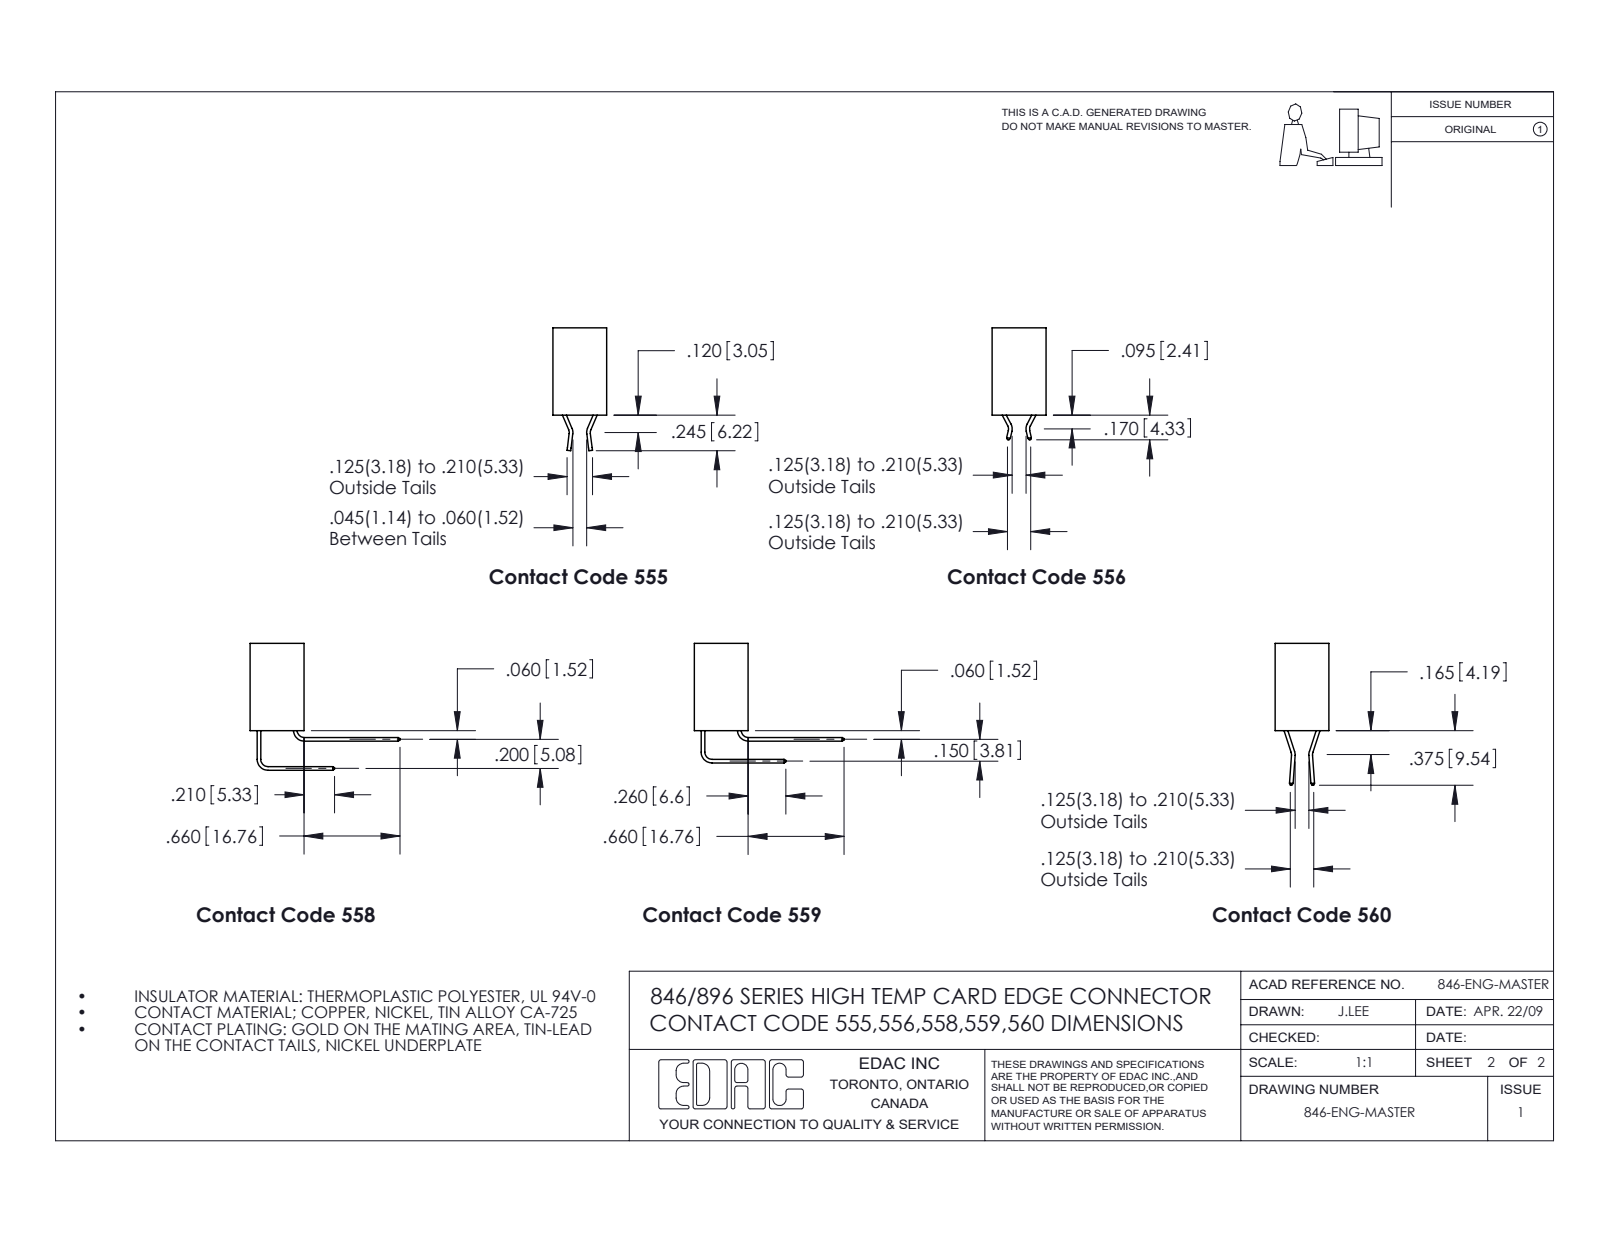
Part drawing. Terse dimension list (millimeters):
name: 345-250-001_345-250-005-103; 346 Part_Flush Mounting Lugs - 0.156 Dia-TI; 346-031-558-107; 345-292-001_558 Tail - 2
written by: SolidWorks 2016 (CONFIG_CONTROL_DESIGN)
unit: mm
bodies: 34 solids, 2042 faces (1410 planar, 616 cylindrical, 16 other)
size: 119 × 22.2 × 14.7
volume: 11 400 mm³; area: 14 790 mm²
holes: 2× ⌀2.5, 2× ⌀3.2, 2× ⌀4, 1× ⌀1.6
bosses: 2× ⌀3.9
rounds: 62× R0.2, 22× R0.3, 6× R0.2, 6× R0.8, 3× R0.7, 2× R0.8, 2× R1, 1× R0.4
face distances: 8.2, 1.2, 9.4, 6.4, 7.6, 0.6, 1.8, 3.8, 5.6, 2.5
hole spacings: 6.2, 107, 112.3
